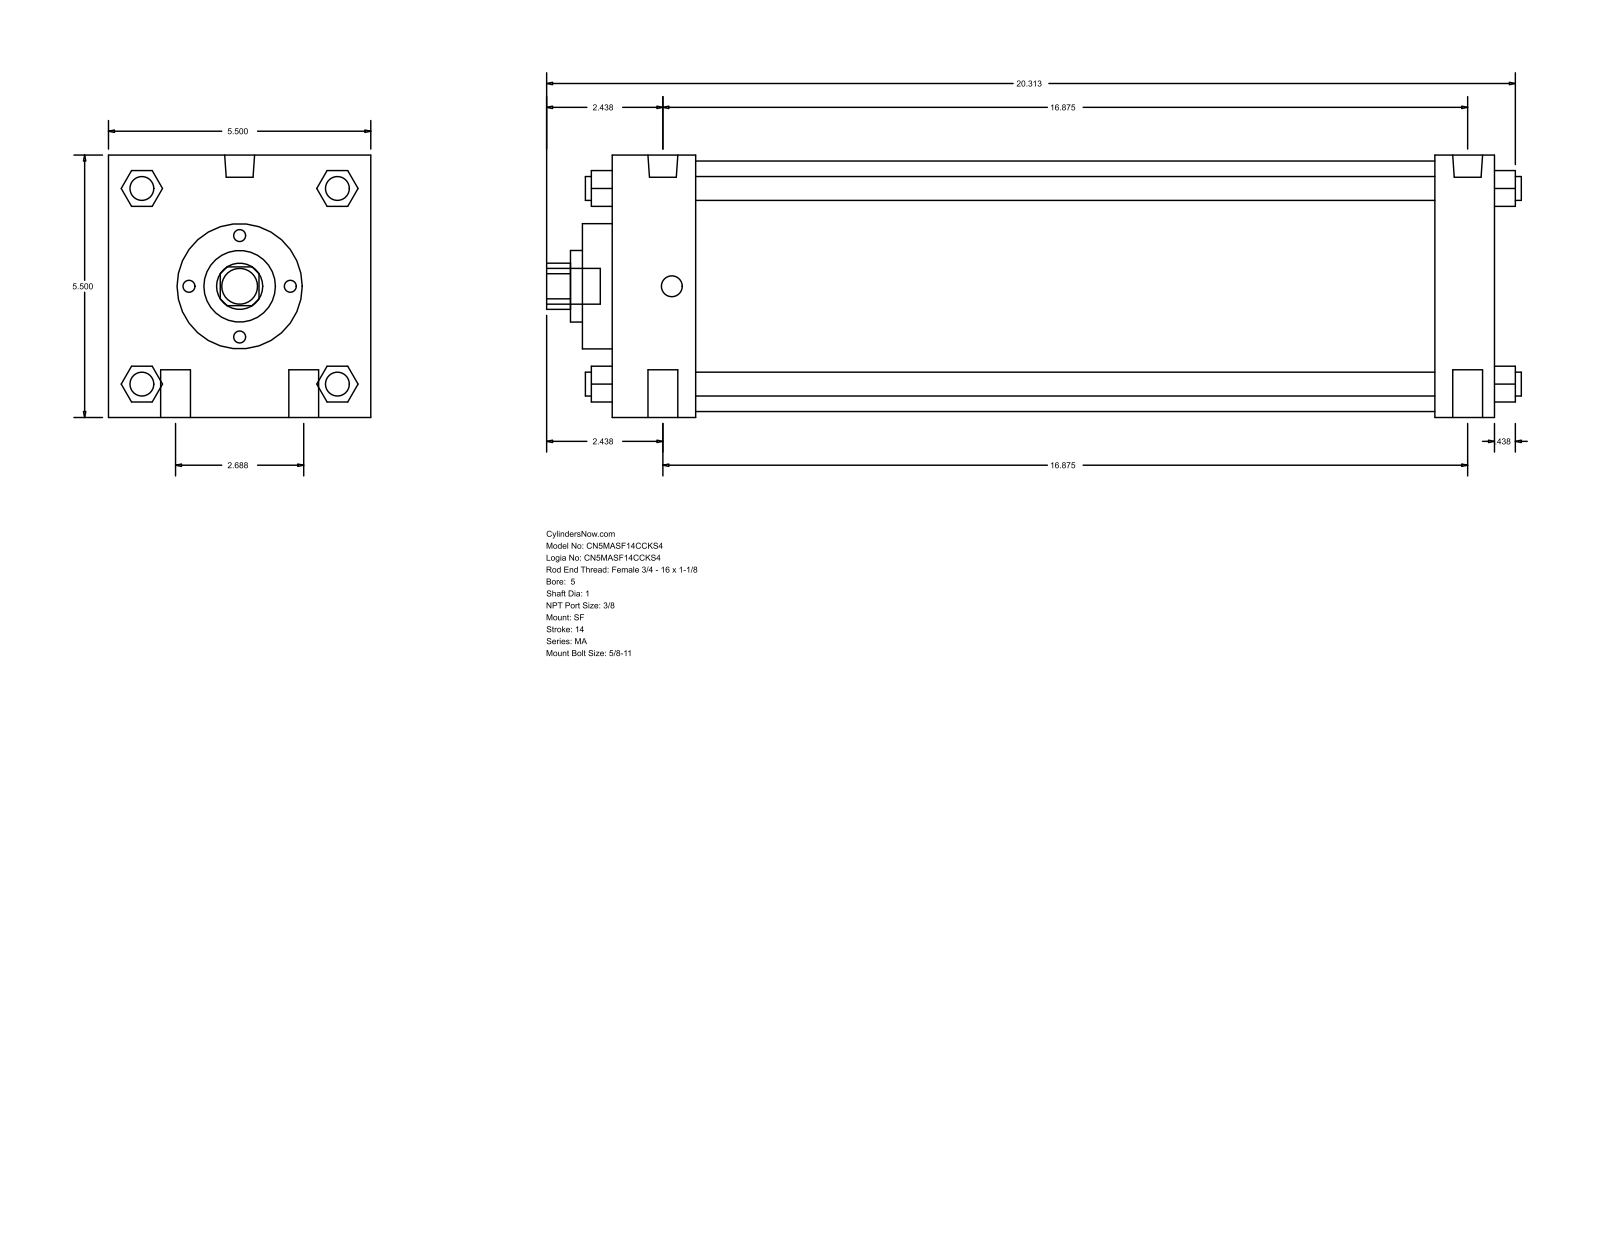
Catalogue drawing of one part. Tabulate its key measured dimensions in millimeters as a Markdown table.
| quantity | value |
| --- | --- |
| part name | MA_SF__0500_1 |
| STEP written by | GSSL Pune (CONFIG_CONTROL_DESIGN) |
| units | millimeters |
| bodies | 0 solids, 126 faces (95 planar, 31 cylindrical, 0 other) |
| overall size | 519.11 × 139.7 × 139.7 |
| round holes (diameter × count) | 25.4 × 1, 38.1 × 1, 66.67 × 1, 133.35 × 1 |
| round bosses / shafts (diameter × count) | 15.88 × 4, 12.7 × 4, 15.93 × 2, 11.11 × 2, 19.05 × 1 |
| partial cylindrical surfaces (radius × count) | 12.29 × 1 |
| main face-to-face distances | 139.7, 469.9, 44.46, 438.15, 393.69, 425.44, 31.75, 15.87, 60.33, 454.02 |
